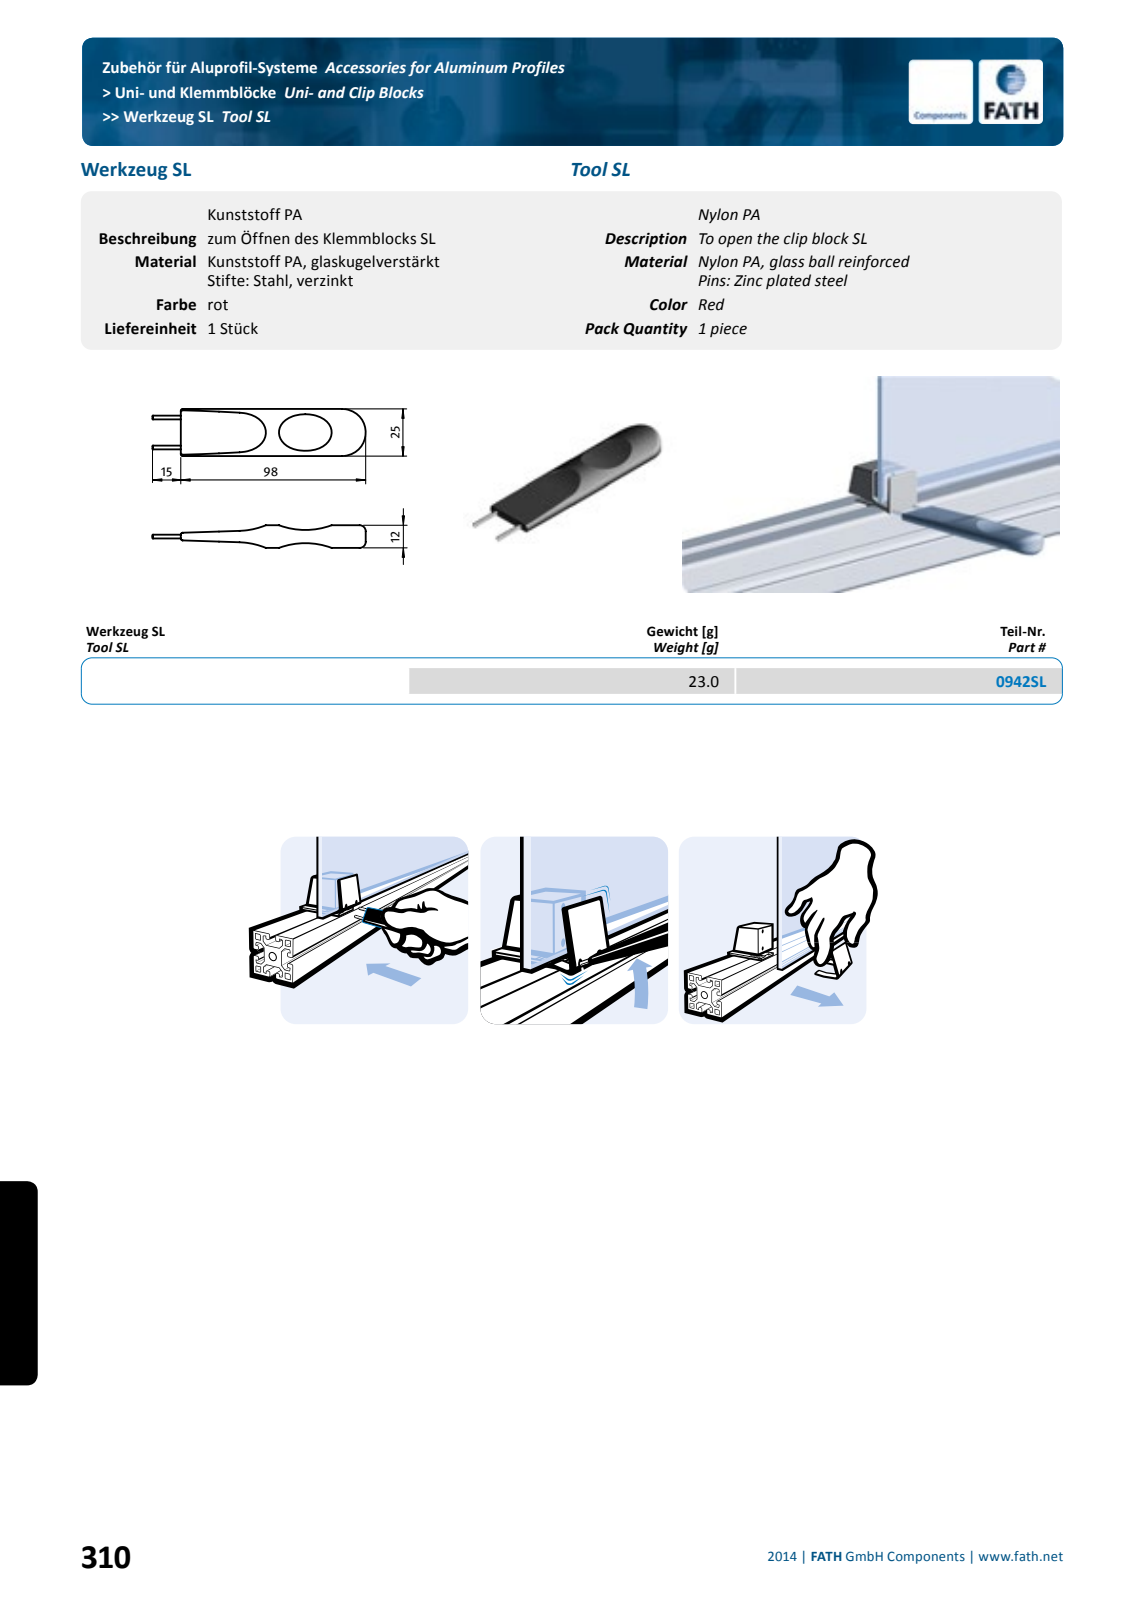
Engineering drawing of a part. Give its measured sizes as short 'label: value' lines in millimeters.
name: fath_0942sl
written by: Spatial InterOp 3D (automotive_design)
unit: mm
bodies: 1 solid, 53 faces (5 planar, 20 cylindrical, 28 other)
size: 115 × 25 × 12.02
volume: 17 639 mm³; area: 6 141 mm²
bosses: 2× ⌀2
rounds: 4× R40, 2× R1, 2× R3.2, 2× R20, 1× R12.5
face distances: 15
